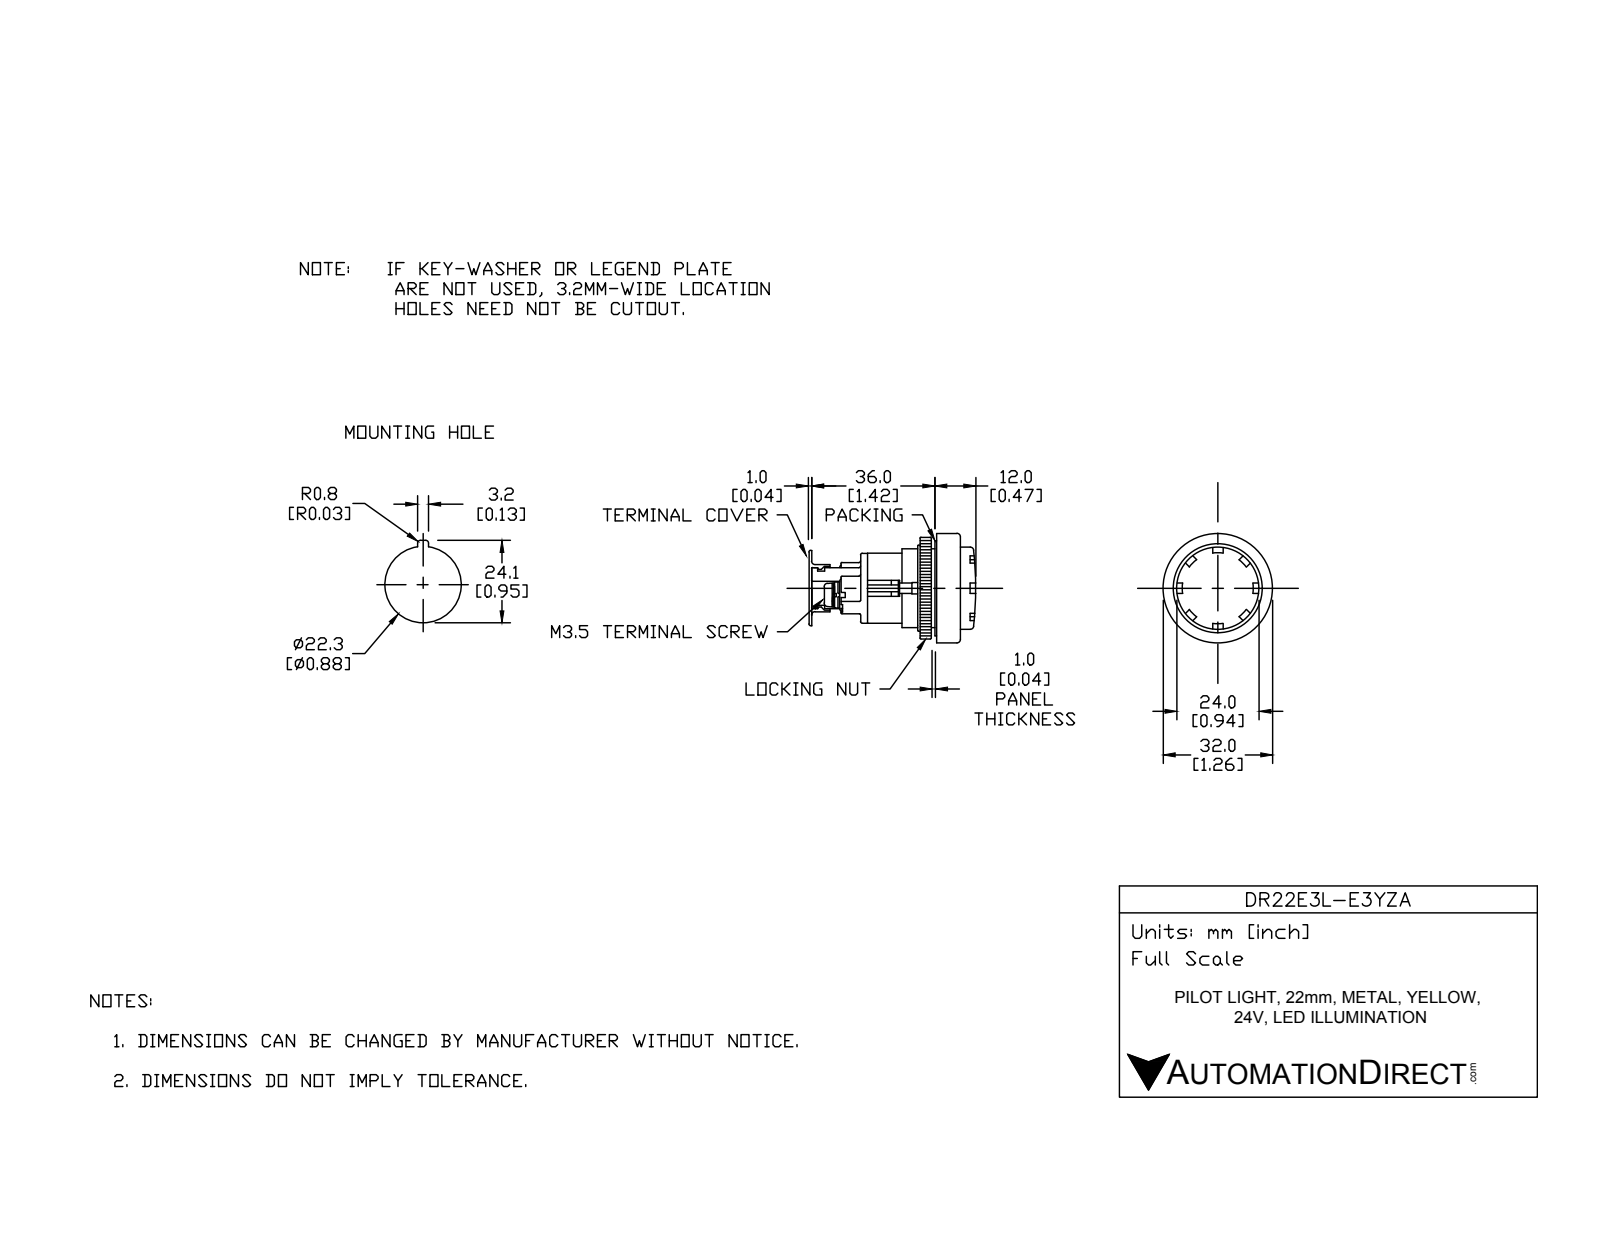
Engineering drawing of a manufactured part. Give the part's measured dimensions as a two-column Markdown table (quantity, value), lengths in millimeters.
| quantity | value |
| --- | --- |
| part name | DR22E3L-E3YZA |
| STEP written by | SolidWorks 2017 (AUTOMOTIVE_DESIGN) |
| units | millimeters |
| bodies | 11 solids, 126 faces (76 planar, 38 cylindrical, 12 other) |
| overall size | 48 × 32 × 32 |
| volume | 19 463 mm³ |
| surface area | 11 440 mm² |
| round holes (diameter × count) | 6.4 × 2, 22 × 1, 25 × 1, 30 × 1 |
| round bosses / shafts (diameter × count) | 5.8 × 2, 32 × 1, 29.7 × 1, 29.5 × 1, 27 × 1, 21.8 × 1 |
| partial cylindrical surfaces (radius × count) | 0.5 × 8 |
| main face-to-face distances | 4, 26, 6, 16, 1, 20, 27, 42, 15, 11 |
| hole center spacings | 6.04, 12.08 |
